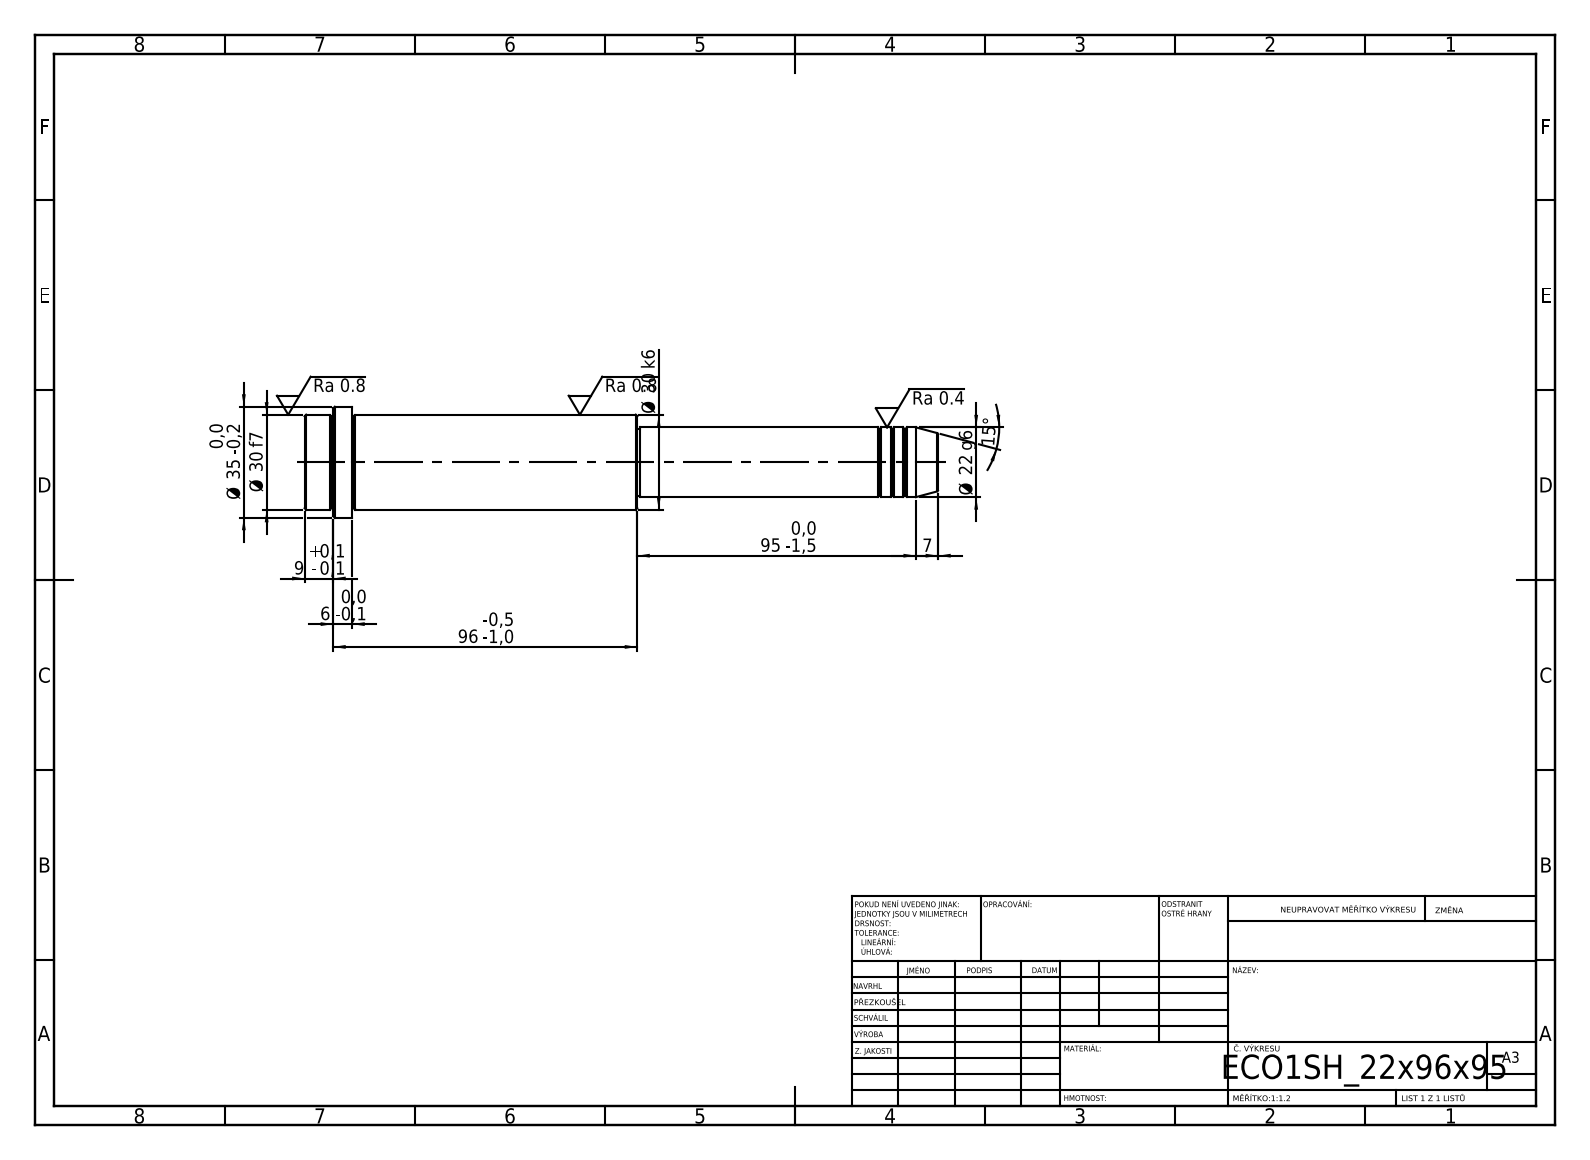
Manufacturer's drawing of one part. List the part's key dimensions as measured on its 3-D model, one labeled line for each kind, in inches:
STEP written by: SolidWorks 2019 (CONFIG_CONTROL_DESIGN)
Units: inches
Bodies: 1 solid, 52 faces (6 planar, 16 cylindrical, 30 other)
Overall size (bounding box): 7.874 × 1.378 × 1.378
Volume: 6.787 in³ · Surface area: 28.7 in²
Round bosses / shafts (diameter × count): ⌀1.378 ×1, ⌀1.181 ×1, ⌀0.866 ×1, ⌀0.827 ×1
Main face-to-face distances: 4.134, 3.543, 0.591, 3.74, 7.283, 7.874, 7.52, 3.78, 0.236, 0.354
